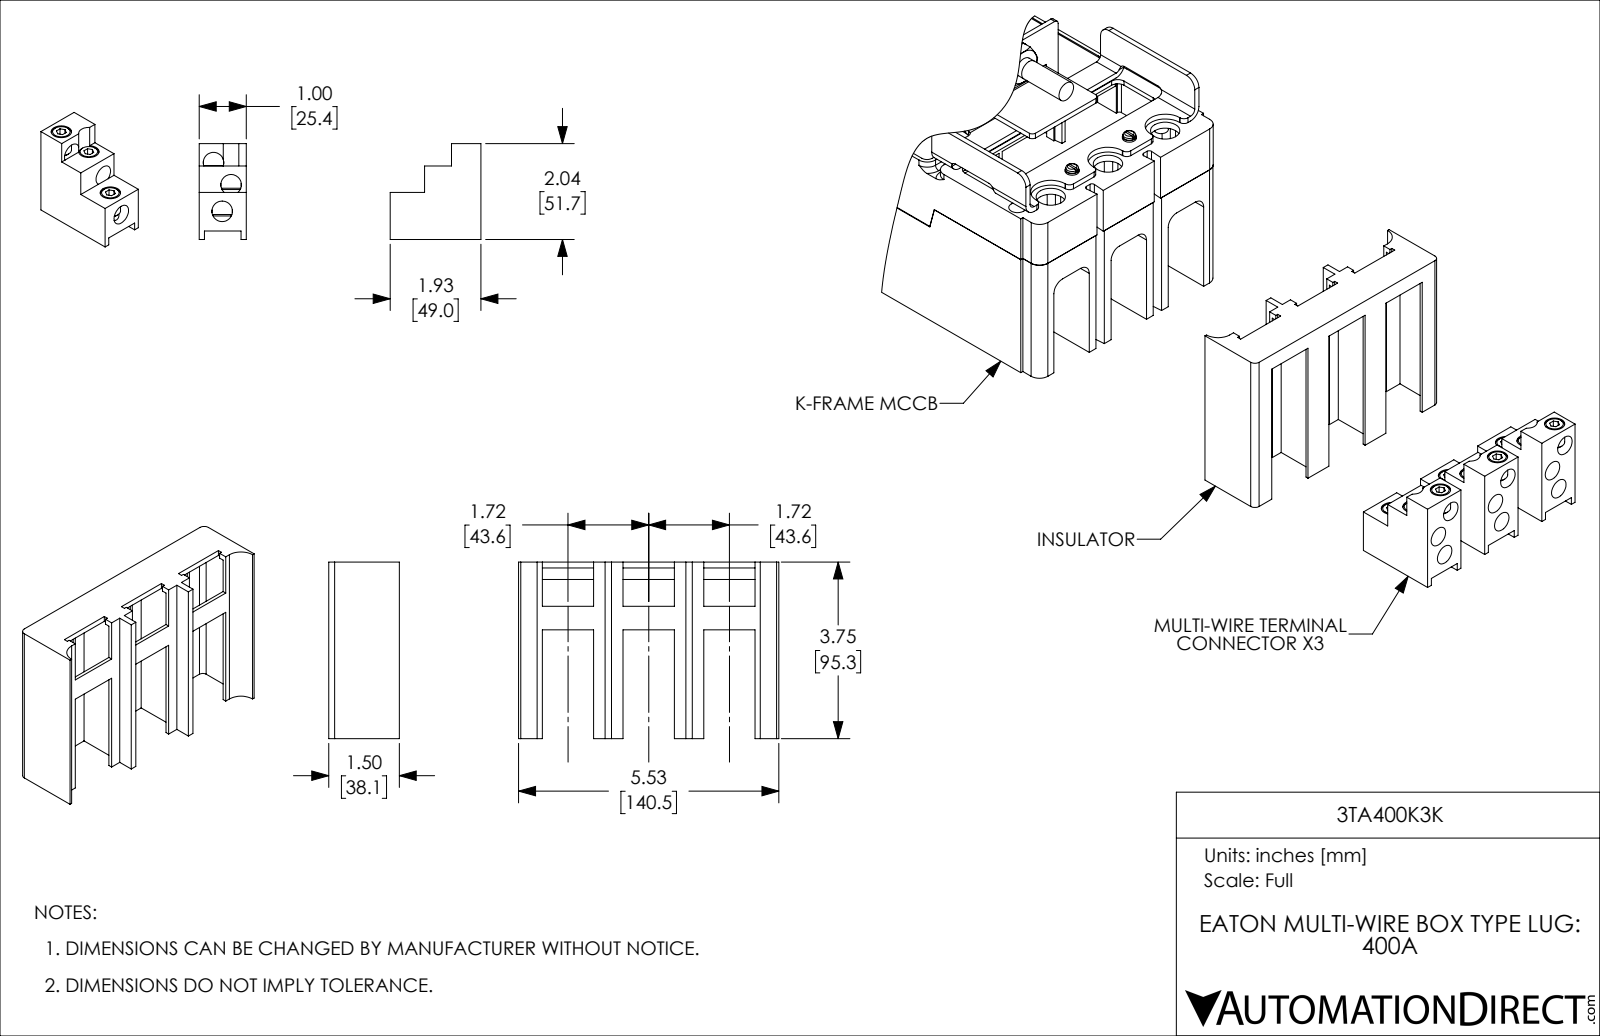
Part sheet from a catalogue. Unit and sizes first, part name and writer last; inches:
Units: inches
Overall size (bounding box): 5.531 × 3.75 × 1.929
Round holes (diameter × count): ⌀0.432 ×9, ⌀0.436 ×9, ⌀0.328 ×3
Partial cylindrical surfaces — rounded edges, fillets, slot ends (radius × count): R0.1 ×2, R0.125 ×2, R0.347 ×2
Main face-to-face distances: 1.715, 1, 1.073, 1.952, 3.579, 0.06, 1.013, 0.1, 5.431, 1.852
Hole centre spacings: 1.715, 1.715, 3.43, 0.018, 0.595, 0.856, 1.05, 1.302
Volume: 10.49 in³ · Surface area: 156 in²
Bodies: 13 solids, 313 faces (211 planar, 66 cylindrical, 36 other)
Part name (STEP PRODUCT): 3TA400K3K_1; 3TA400K3K; 3TA400K3K_2
STEP written by: SolidWorks 2019 (CONFIG_CONTROL_DESIGN)
